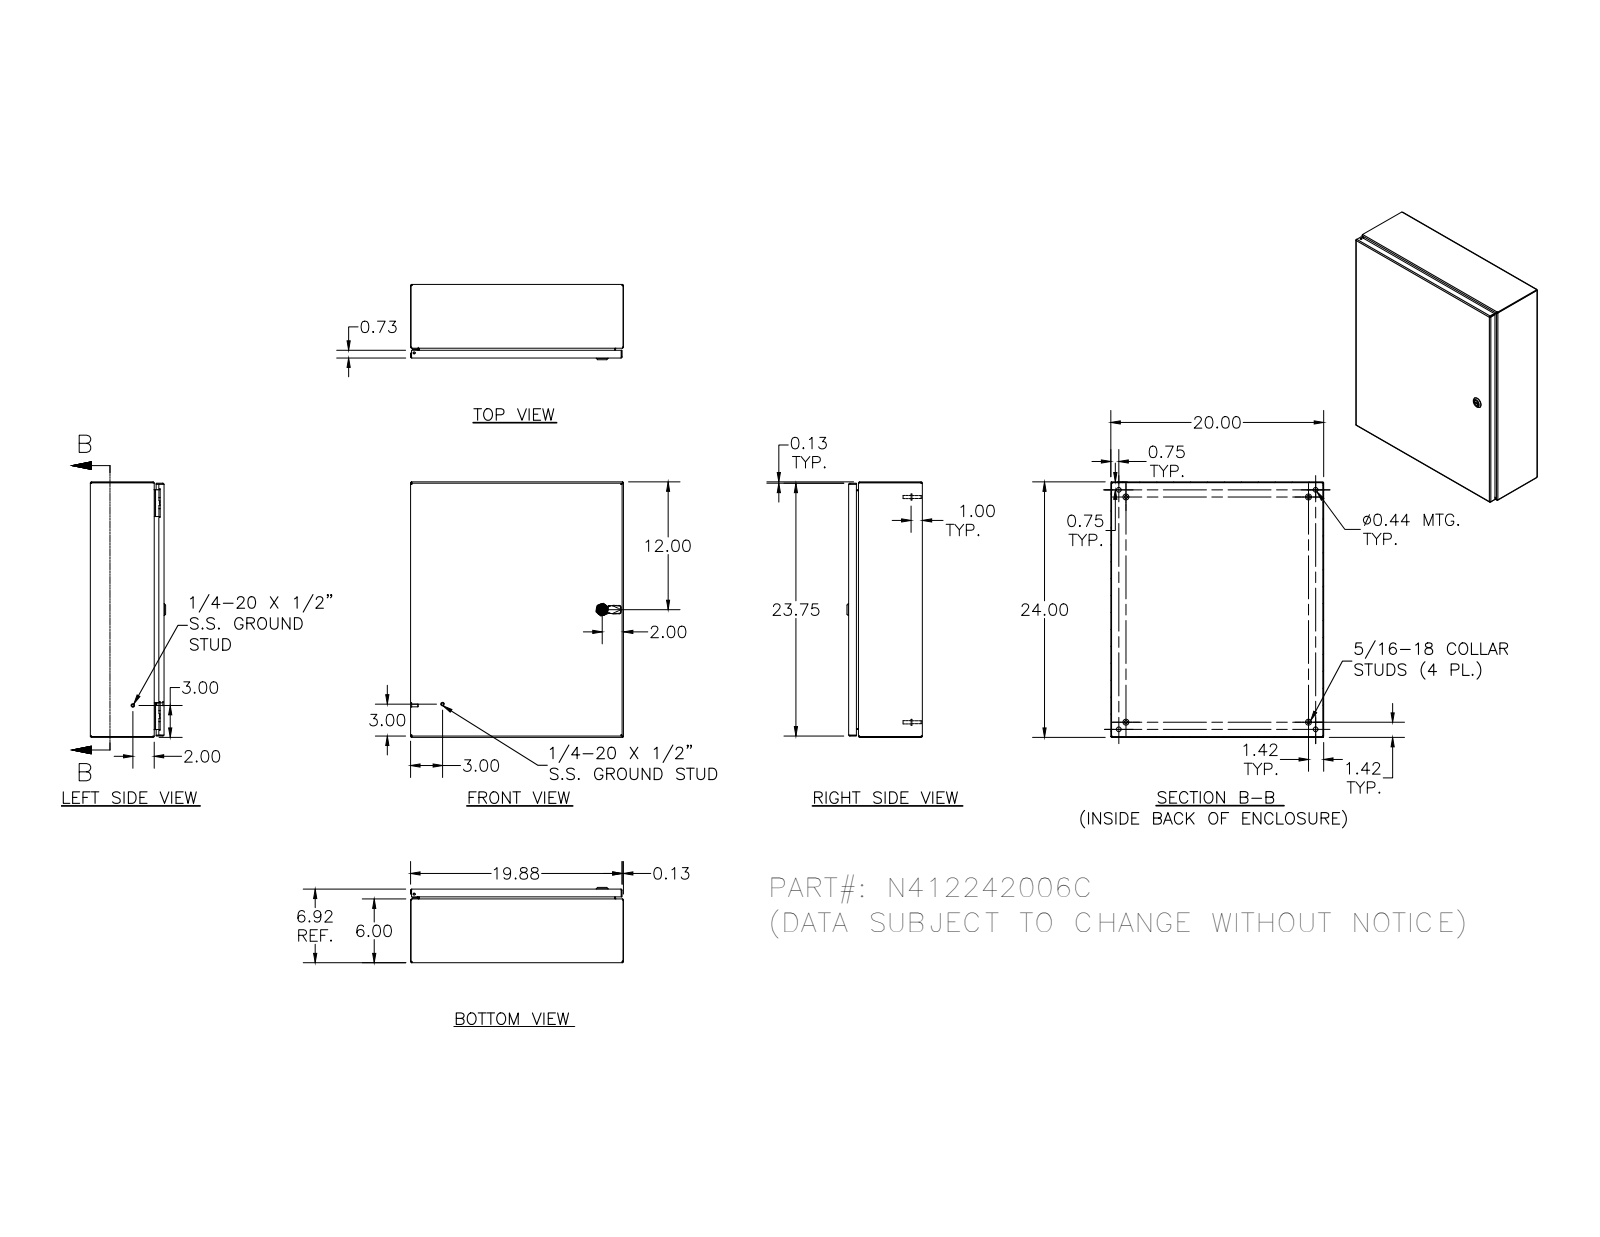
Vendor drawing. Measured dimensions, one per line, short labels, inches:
name: N412242006C
written by: SolidWorks 2018 (AUTOMOTIVE_DESIGN)
unit: in
bodies: 33 solids, 1449 faces (530 planar, 547 cylindrical, 372 other)
size: 24 × 20 × 7.075
volume: 123.3 in³; area: 3 350 in²
holes: 5× ⌀0.188, 4× ⌀0.093, 4× ⌀0.152, 4× ⌀0.167, 4× ⌀0.172, 4× ⌀0.437, 2× ⌀0.156, 1× ⌀0.187, 1× ⌀0.197, 1× ⌀0.315, 1× ⌀0.394, 1× ⌀0.402
bosses: 10× ⌀0.25, 4× ⌀0.563, 4× ⌀0.36, 4× ⌀0.32, 4× ⌀0.3, 4× ⌀0.256, 4× ⌀0.164, 4× ⌀0.131
rounds: 30× R0.012, 30× R0.031, 26× R0.05, 20× R0.105, 18× R0.016, 16× R0.125, 13× R0.02, 8× R0.032
face distances: 0.074, 6.843, 6.769, 6.917, 0.074, 19.926, 20, 19.852, 19.926, 23.926
hole spacings: 20, 0.66, 0.656, 1.307, 1.965, 19.34, 20.66, 1.619
